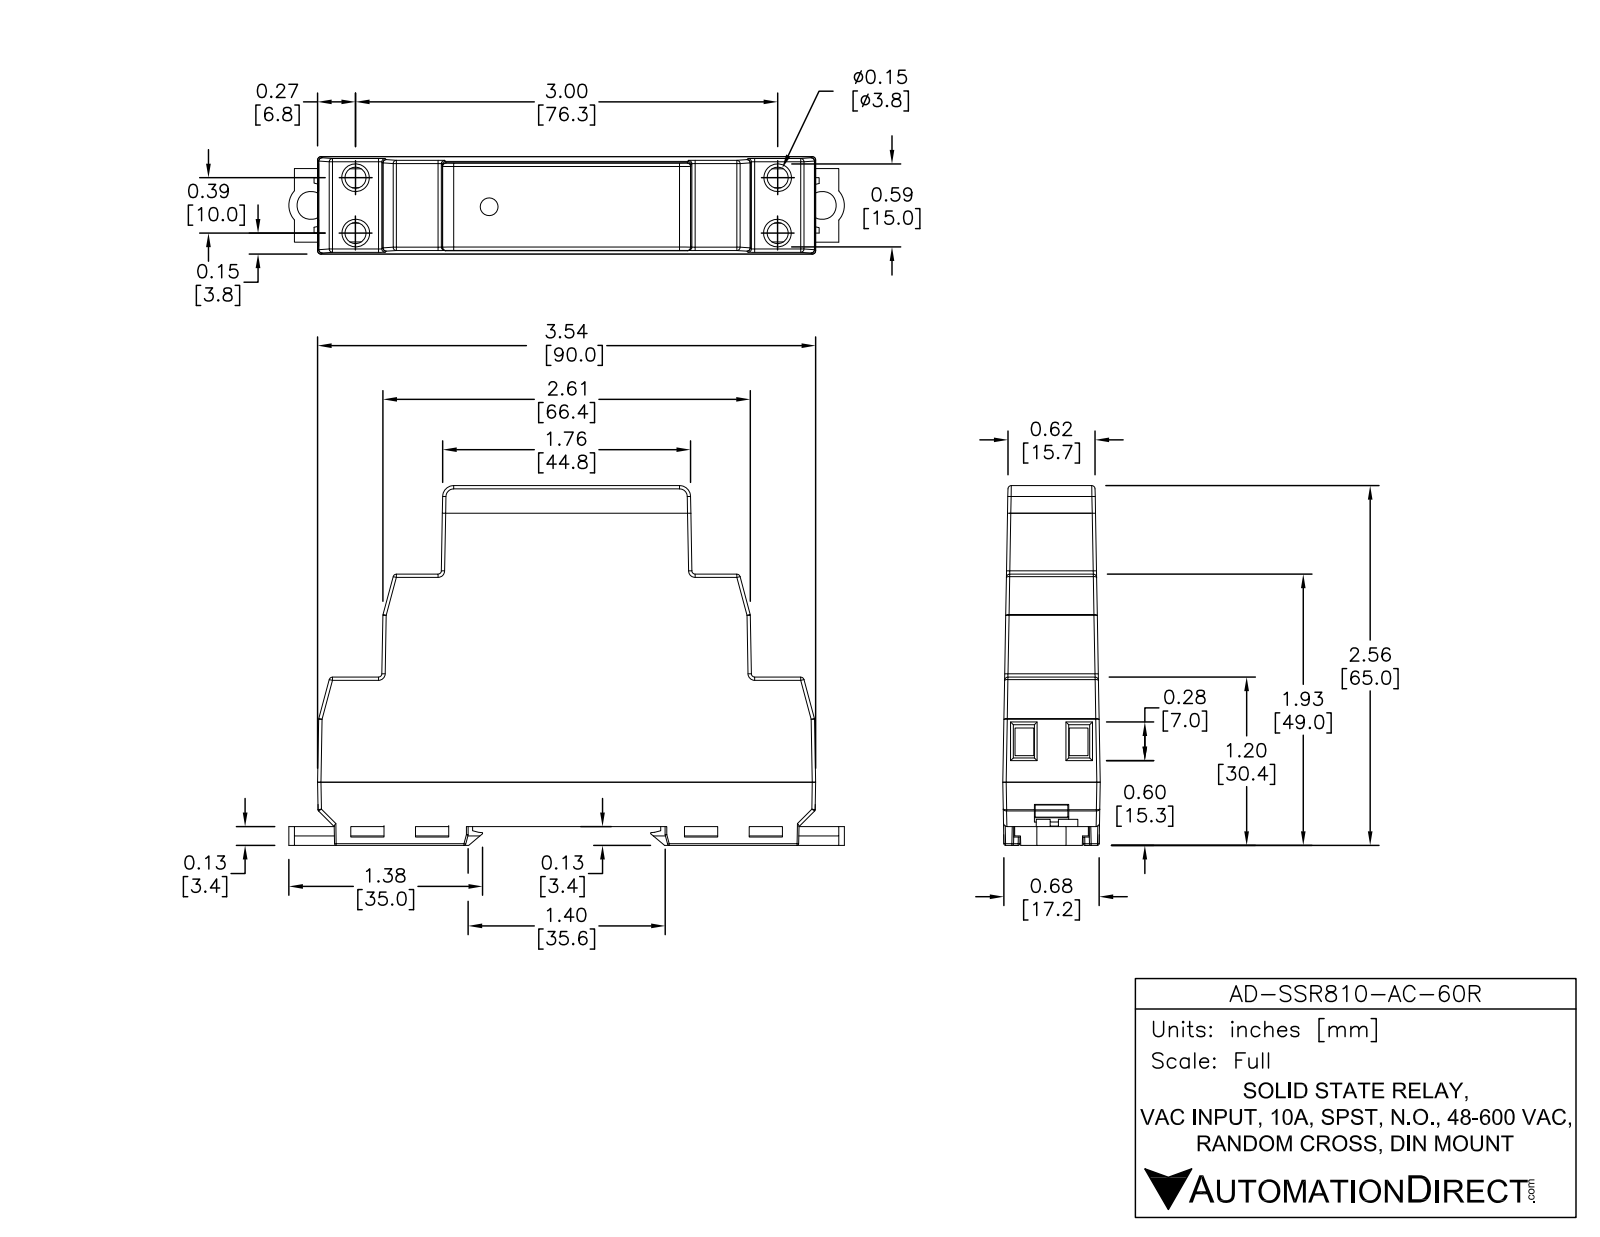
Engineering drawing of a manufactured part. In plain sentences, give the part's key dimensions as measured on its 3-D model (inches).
The part is named "AD-SSR810-AC-60R". Its 3-D file was written by "SolidWorks 2013 (AUTOMOTIVE_DESIGN)". It is 1 solid with 840 faces: 492 planar, 78 cylindrical and 270 other. Overall it measures 3.924 by 2.616 by 0.685 inches. Its volume is 4.605 cubic inches and its surface area 24.23 square inches. Round holes: 4 of diameter 0.19, 2 of diameter 0.2. Round bosses or shafts: 1 of diameter 0.105. Partial cylindrical surfaces (rounded edges, fillets, slot ends): 41 of radius 0.015, 2 of radius 0.06, 2 of radius 0.172. The main face-to-face distances are 2.525, 0.049, 2.574, 0.425, 2.215, 0.025, 0.05, 1.934, 1.885, 0.64. The hole center spacings are 0.338, 3.3, 0.364, 3.01, 3.032, 3.58.
